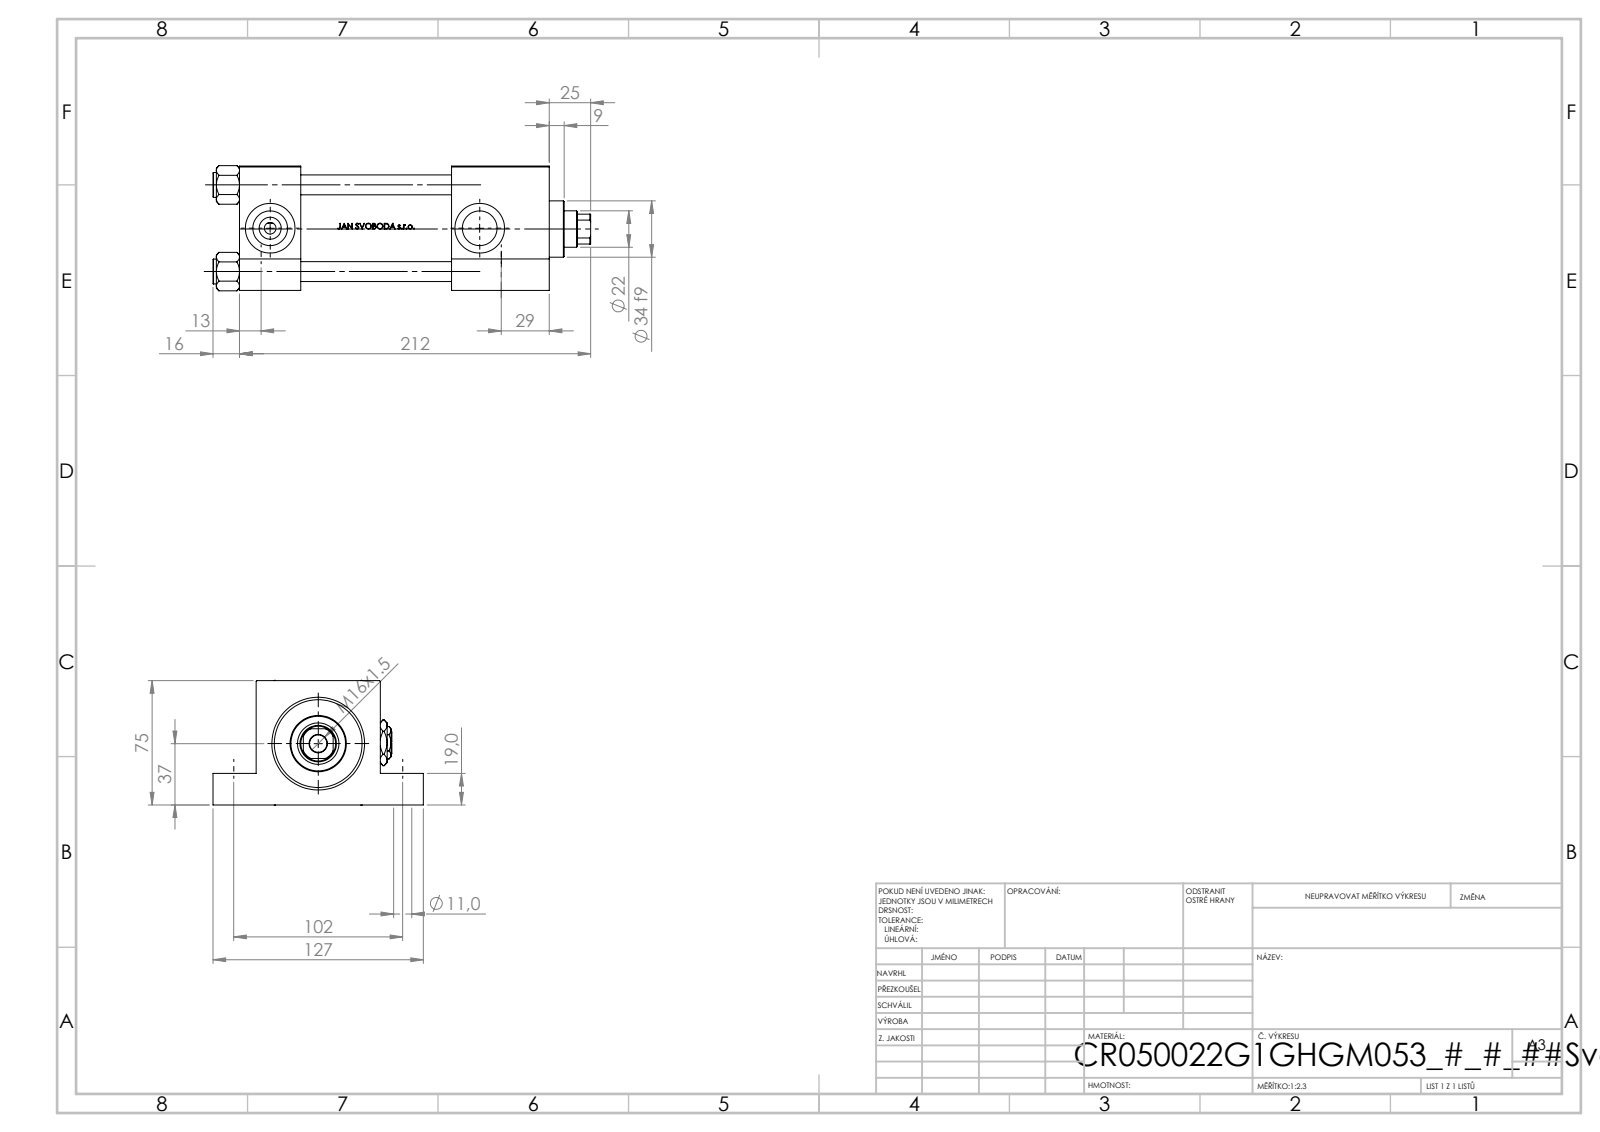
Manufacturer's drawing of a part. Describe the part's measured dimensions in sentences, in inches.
The part is named "NUT_M5_G; Zatka_pro_OIL_PORT; V215_VC_A; V215CR_G_TYCINKA (+2 more)". Its 3-D file was written by "SolidWorks 2019 (CONFIG_CONTROL_DESIGN)". It is 12 solids with 1134 faces: 454 planar, 128 cylindrical and 552 other. Overall it measures 8.976 by 5 by 2.974 inches. Its volume is 48.6 cubic inches and its surface area 278.3 square inches. Round holes: 4 of diameter 0.433, 4 of diameter 0.472, 2 of diameter 0.276, 2 of diameter 0.825, 2 of diameter 1.181, 1 of diameter 0.413, 1 of diameter 0.866, 1 of diameter 0.984, 1 of diameter 1.614, 1 of diameter 1.969, 1 of diameter 2.087. Round bosses or shafts: 4 of diameter 0.591, 1 of diameter 2.205, 1 of diameter 1.339. Partial cylindrical surfaces (rounded edges, fillets, slot ends): 1 of radius 0.413. The main face-to-face distances are 2.953, 1.457, 7.362, 5.906, 3.583, 0.748, 2.205, 5.039, 2.323, 1.024. The hole center spacings are 2.059, 1.442, 1.47, 2.912, 4.016, 5.709, 6.98, 4.98.
